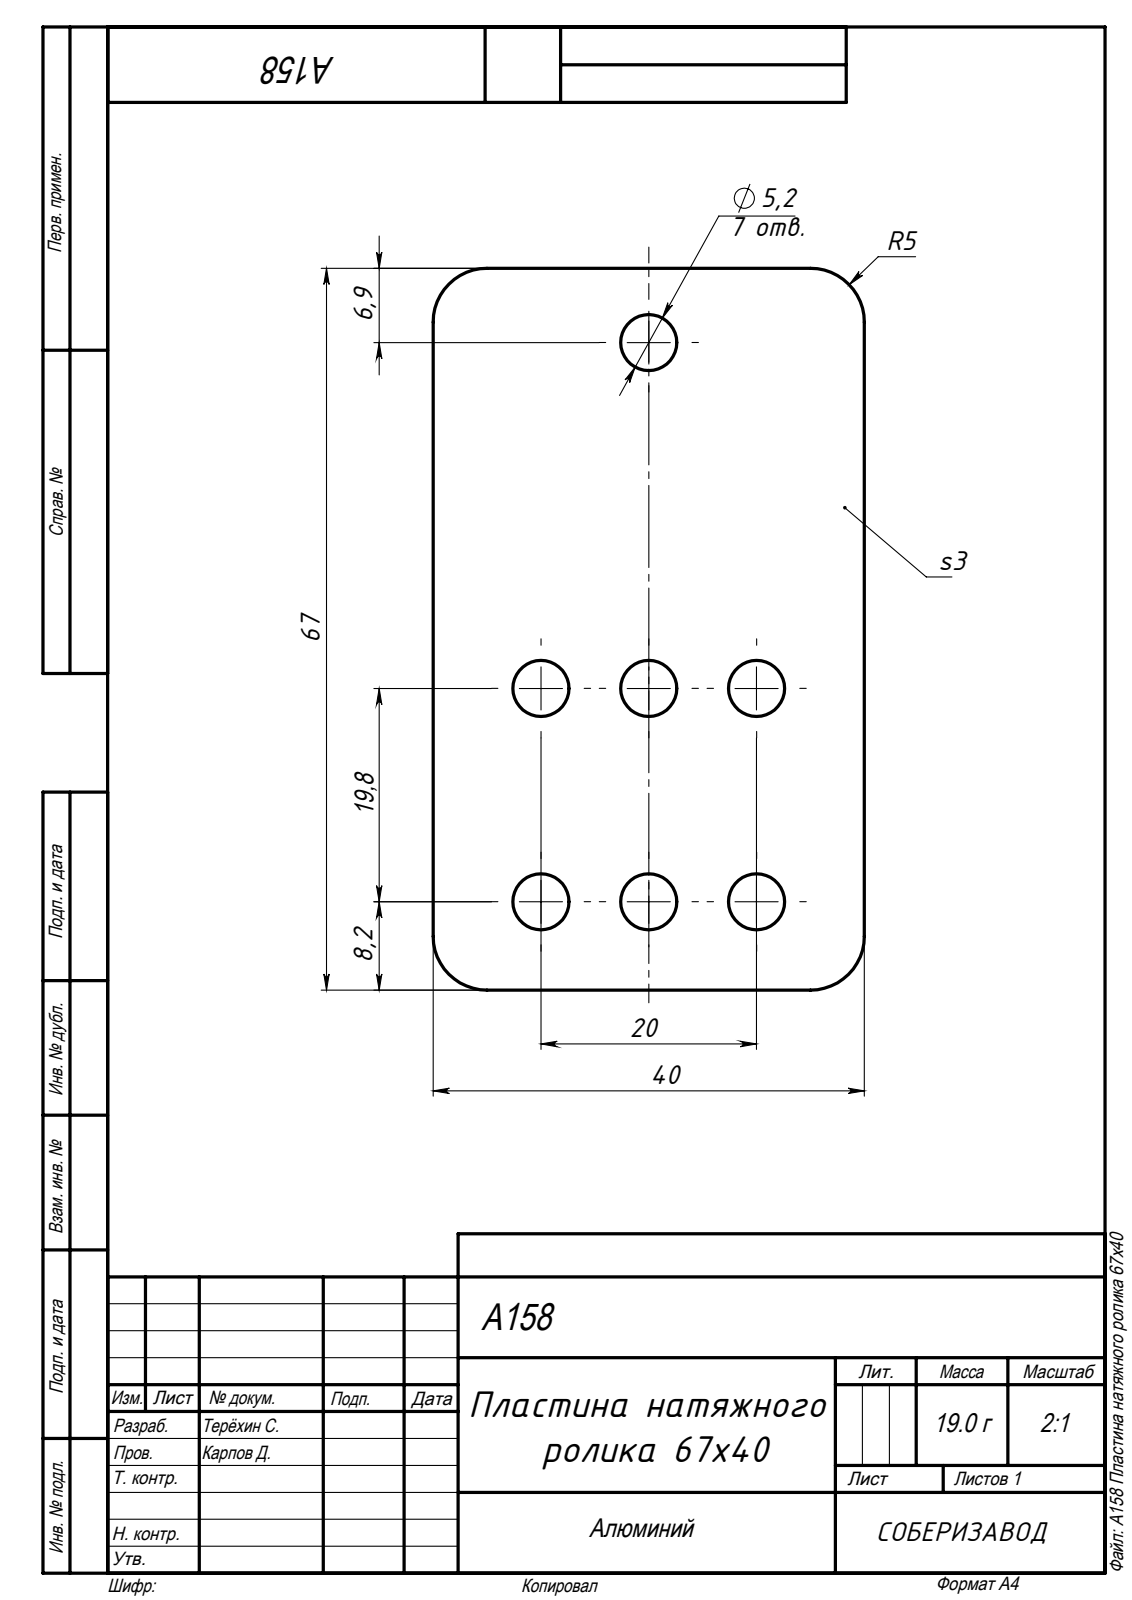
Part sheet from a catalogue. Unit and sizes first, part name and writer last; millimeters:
Units: millimetres
Overall size (bounding box): 67 × 40 × 3
Round holes (diameter × count): ⌀5.2 ×7
Partial cylindrical surfaces — rounded edges, fillets, slot ends (radius × count): R5 ×4
Main face-to-face distances: 3, 40, 67
Hole centre spacings: 10, 22.18, 19.8, 20, 28.14, 33.62, 52.85, 32.1
Volume: 7 530 mm³ · Surface area: 5 979 mm²
Bodies: 1 solid, 24 faces (6 planar, 18 cylindrical, 0 other)
Part name (STEP PRODUCT): A158 Пластина натяжного ролика 67x40
STEP written by: SolidWorks 2018 (AUTOMOTIVE_DESIGN)
